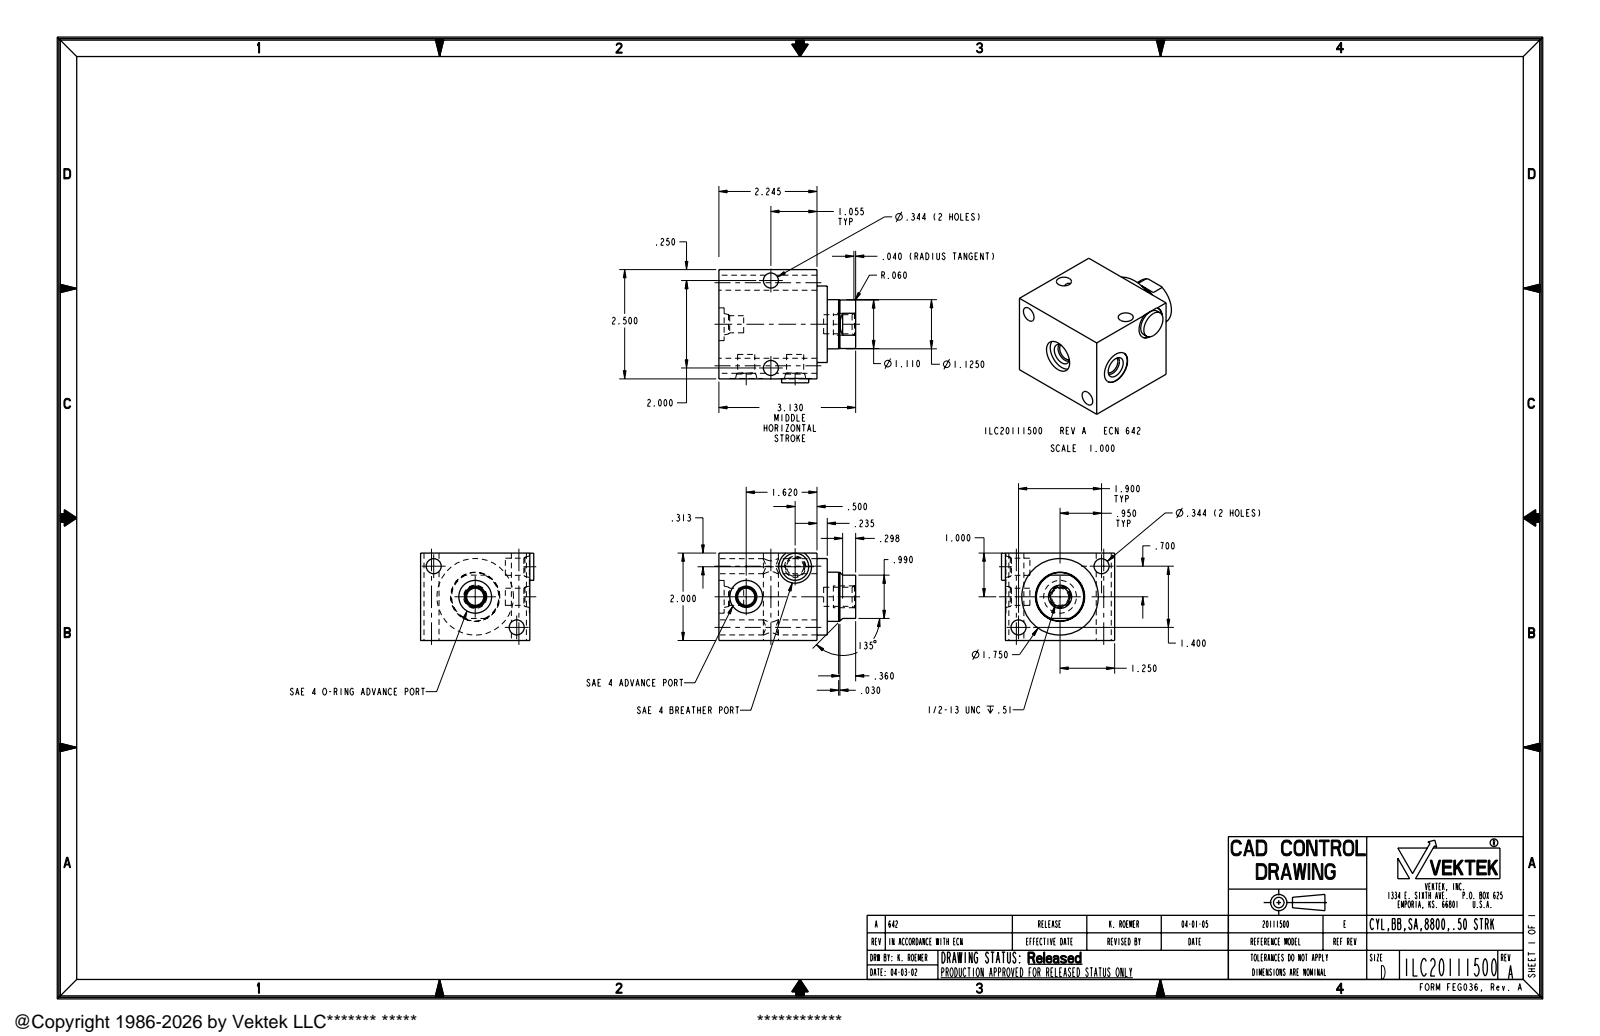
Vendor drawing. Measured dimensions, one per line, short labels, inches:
name: ILC20111500
written by: PRO/ENGINEER BY PARAMETRIC TECHNOLOGY CORPORATION, 2004290 (AUTOMOTIVE_DESIGN_CC2)
unit: in
bodies: 1 solid, 75 faces (22 planar, 35 cylindrical, 18 other)
size: 3.13 × 2.59 × 2
volume: 11.33 in³; area: 45.71 in²
holes: 4× ⌀0.344, 3× ⌀0.392, 3× ⌀0.75, 1× ⌀0.437
bosses: 1× ⌀1.75, 1× ⌀1.125, 1× ⌀1.11, 1× ⌀0.62, 1× ⌀0.5
face distances: 2, 2.5, 2.245, 0.235, 2.48, 0.65, 0.885, 3.13, 2.49, 0.09
hole spacings: 1.18, 1.314, 2, 2.36
